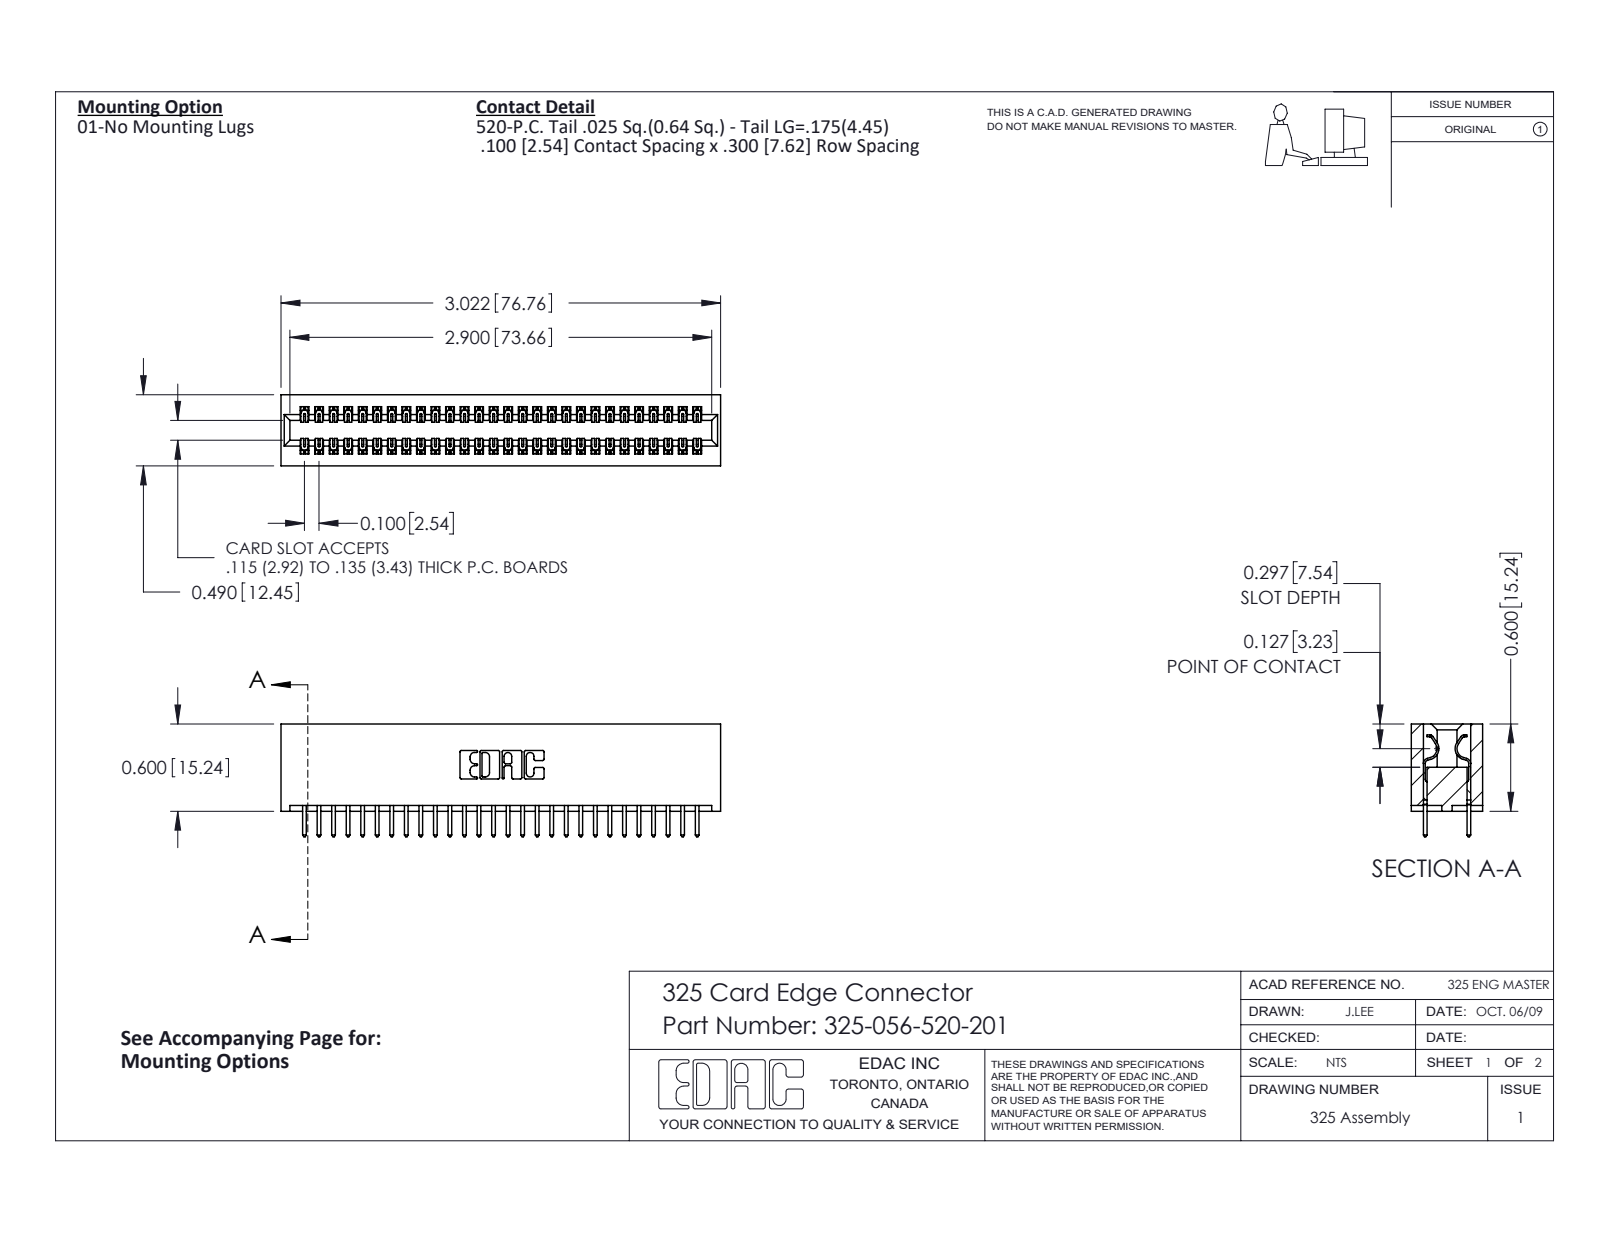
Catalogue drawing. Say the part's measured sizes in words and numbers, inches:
The part is named "325-056-520-201; 325-292-001_325-293-120; 325 Part_Lugless". Its 3-D file was written by "SolidWorks 2016 (CONFIG_CONTROL_DESIGN)". It is 57 solids with 3018 faces: 2082 planar, 936 cylindrical and 0 other. Overall it measures 3.022 by 0.775 by 0.49 inches. Its volume is 0.634 cubic inches and its surface area 19.81 square inches. Partial cylindrical surfaces (rounded edges, fillets, slot ends): 84 of radius 0.006, 56 of radius 0.01, 22 of radius 0.01, 6 of radius 0.007, 6 of radius 0.031, 3 of radius 0.026, 2 of radius 0.014, 2 of radius 0.022. The main face-to-face distances are 0.083, 0.407, 0.3, 0.49, 0.107, 0.383, 0.025, 0.325, 0.275, 0.56.
